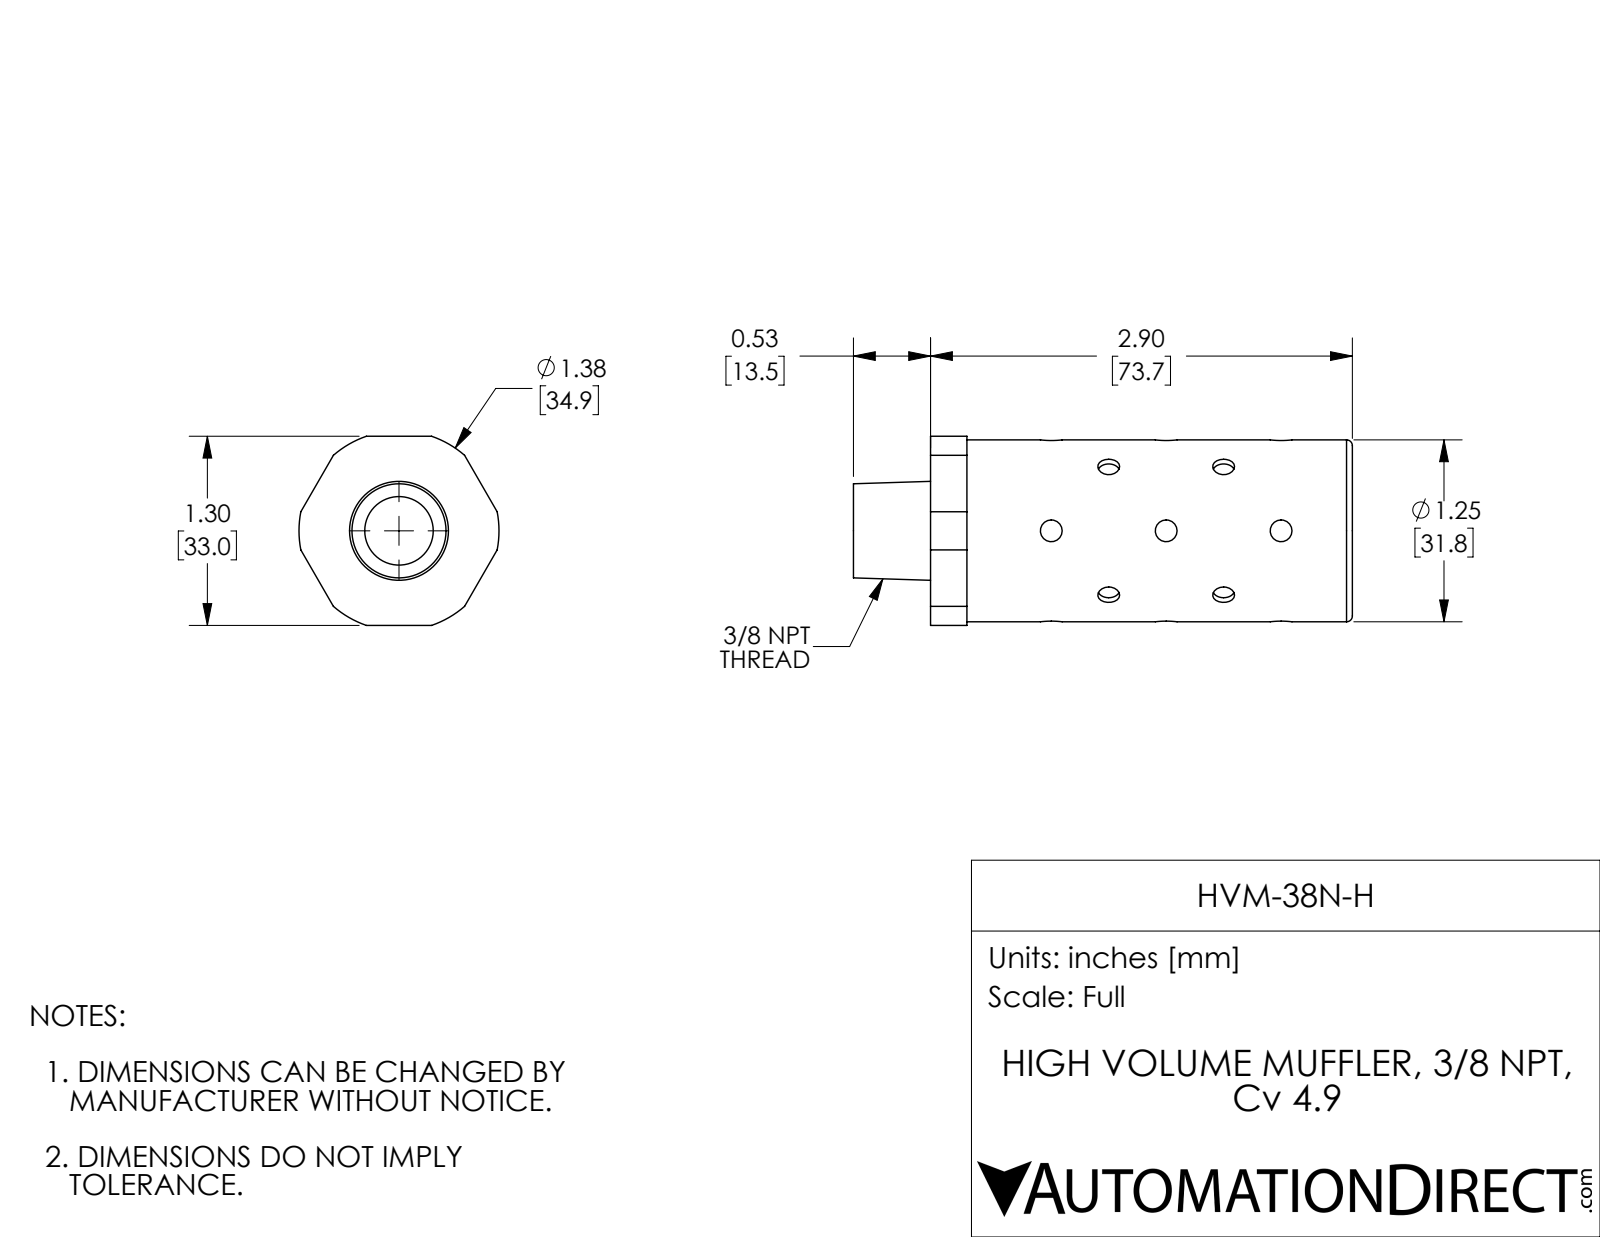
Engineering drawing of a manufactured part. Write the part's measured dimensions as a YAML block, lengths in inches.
part_name: "HVM-38N-H"
step_written_by: "SolidWorks 2017 (AUTOMOTIVE_DESIGN)"
units: inches
bodies: {solids: 1, faces: 86, planar: 31, cylindrical: 51, other: 4}
overall_size: [3.43, 1.375, 1.3]
volume: 3.217
surface_area: 20.47
round_holes:
  - {diameter: 0.15, count: 10}
  - {diameter: 0.471, count: 1}
round_bosses_or_shafts:
  - {diameter: 1.25, count: 1}
partial_cylinders:
  - {radius: 0.687, count: 1}
face_to_face_distances: [2.9, 0.25, 2.65, 1.3, 2.4, 0.53, 0.78, 3.18, 3.43, 0.075]
hole_center_spacings: [0.79, 0.79, 1.58]
